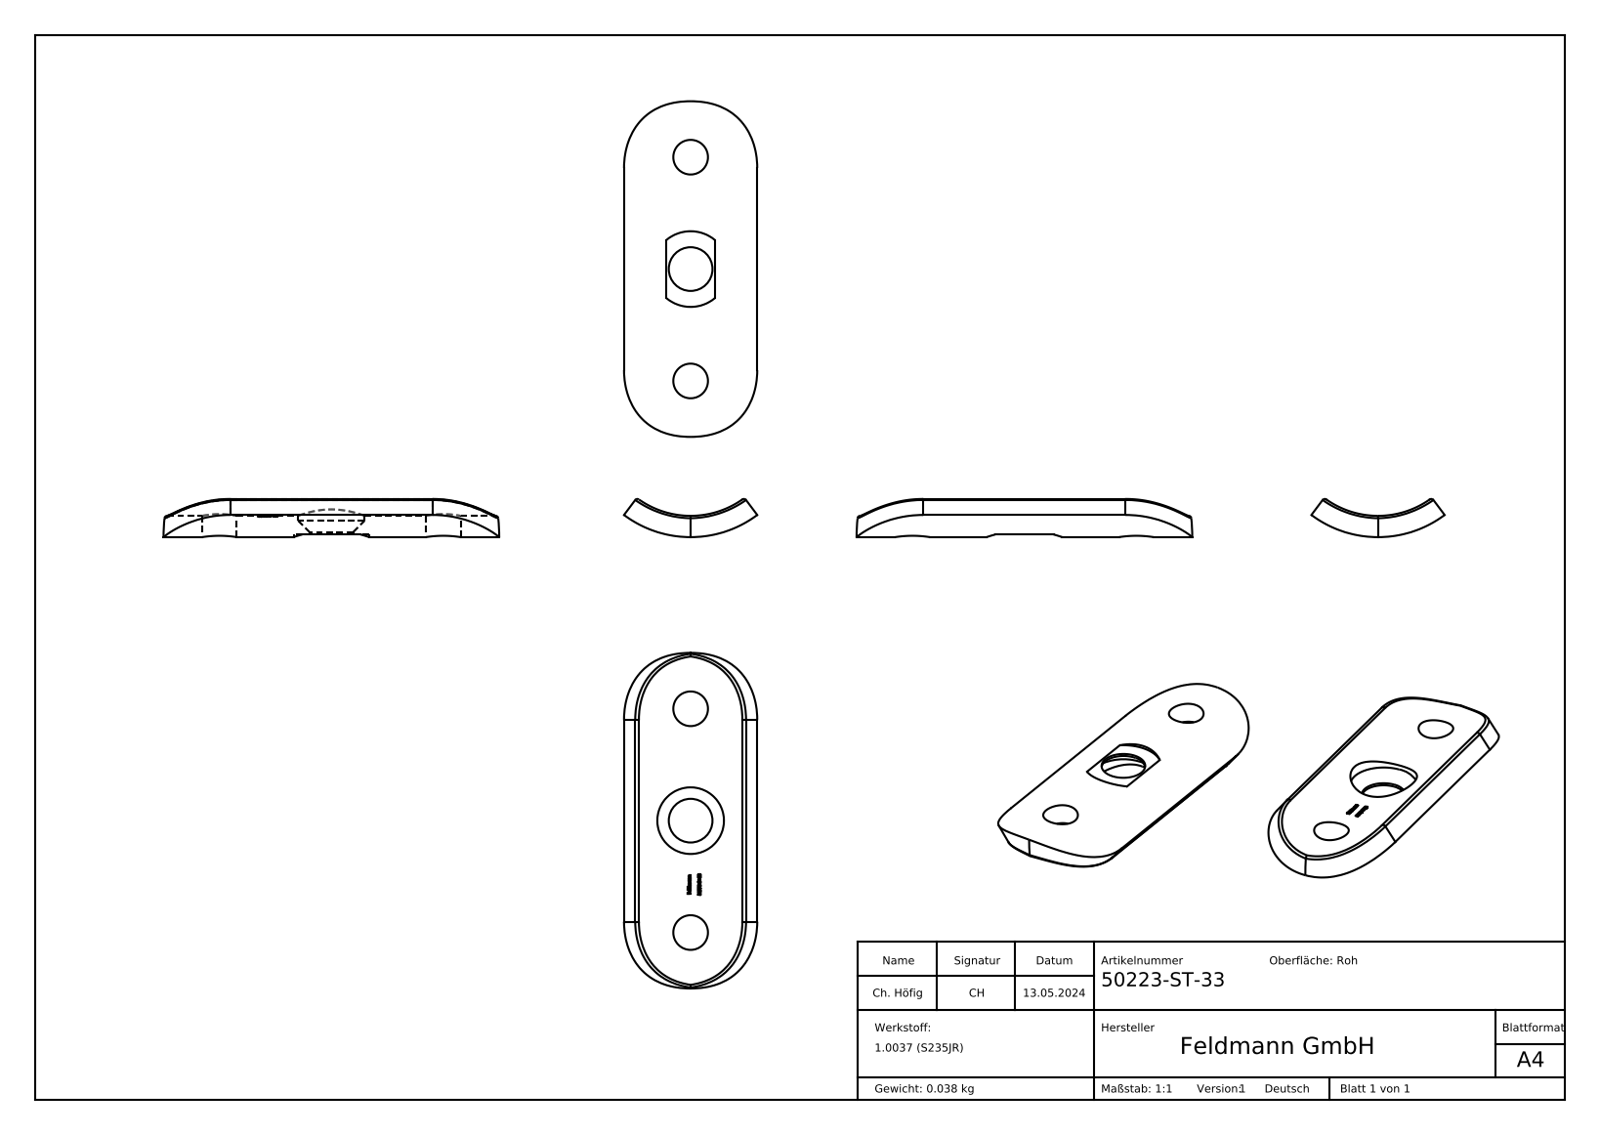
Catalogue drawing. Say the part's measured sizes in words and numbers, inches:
The part is named "50223-ST-33". Its 3-D file was written by "SolidWorks 2015 (CONFIG_CONTROL_DESIGN)". It is 1 solid with 284 faces: 121 planar, 23 cylindrical and 140 other. Overall it measures 2.48 by 1.024 by 0.294 inches. Its volume is 0.315 cubic inches and its surface area 5.465 square inches. Round holes: 2 of diameter 0.256, 1 of diameter 0.315, 1 of diameter 0.492. Partial cylindrical surfaces (rounded edges, fillets, slot ends): 4 of radius 0.512, 2 of radius 0.02, 1 of radius 0.28, 1 of radius 0.663, 1 of radius 0.821. The main face-to-face distances are 0.134, 0.021, 0.066, 0.073, 0.075, 0.047, 0.019, 0.019, 0.026, 0.014. The hole center spacings are 0.846, 1.693.
